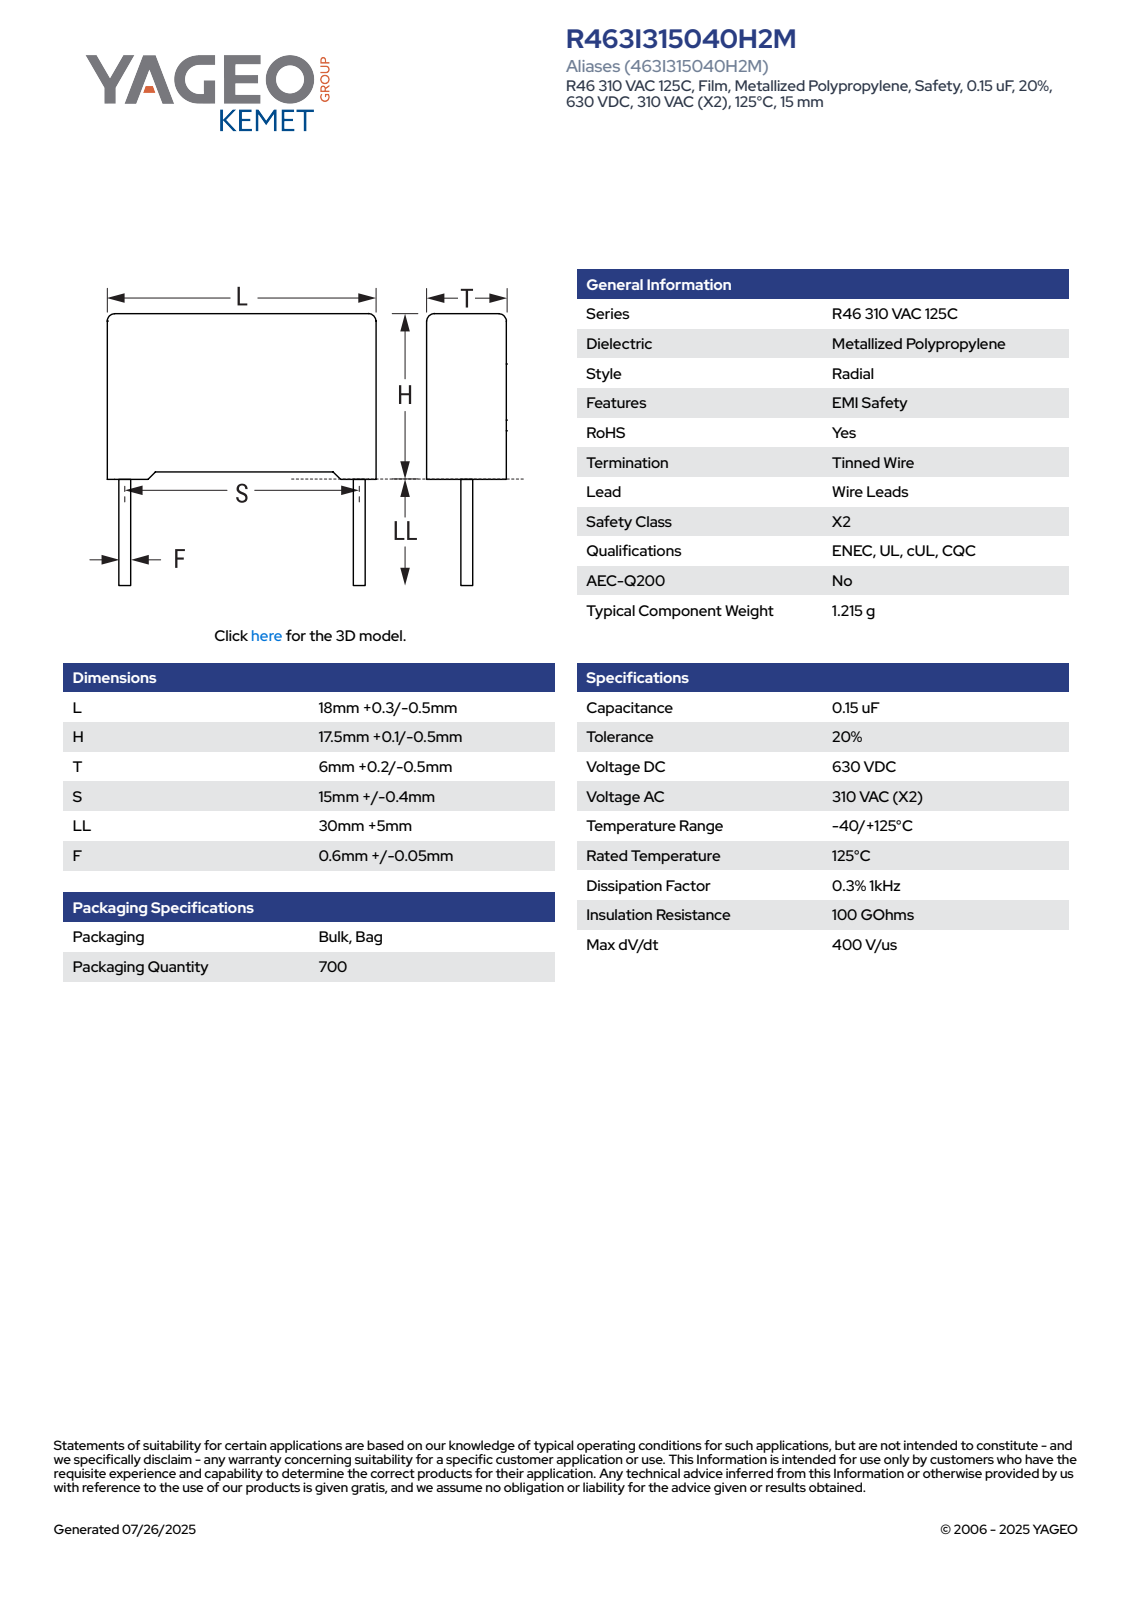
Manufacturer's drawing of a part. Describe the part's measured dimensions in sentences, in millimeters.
The part is named "CFR_RB2_18X12X6_L18.3H17.6T6.2S15LL35F0.65". Its 3-D file was written by "SolidWorks 2021 (AUTOMOTIVE_DESIGN)". It is 4 solids with 85 faces: 77 planar, 8 cylindrical and 0 other. Overall it measures 52.6 by 18 by 6.21 millimeters. Its volume is 1 914 cubic millimeters and its surface area 1 240 square millimeters. Round bosses or shafts: 2 of diameter 0.65. Partial cylindrical surfaces (rounded edges, fillets, slot ends): 4 of radius 0.5. The main face-to-face distances are 6.2, 18, 16.85, 0.6, 0.75, 16.99, 0.61, 17.6, 5.6, 17.4.
